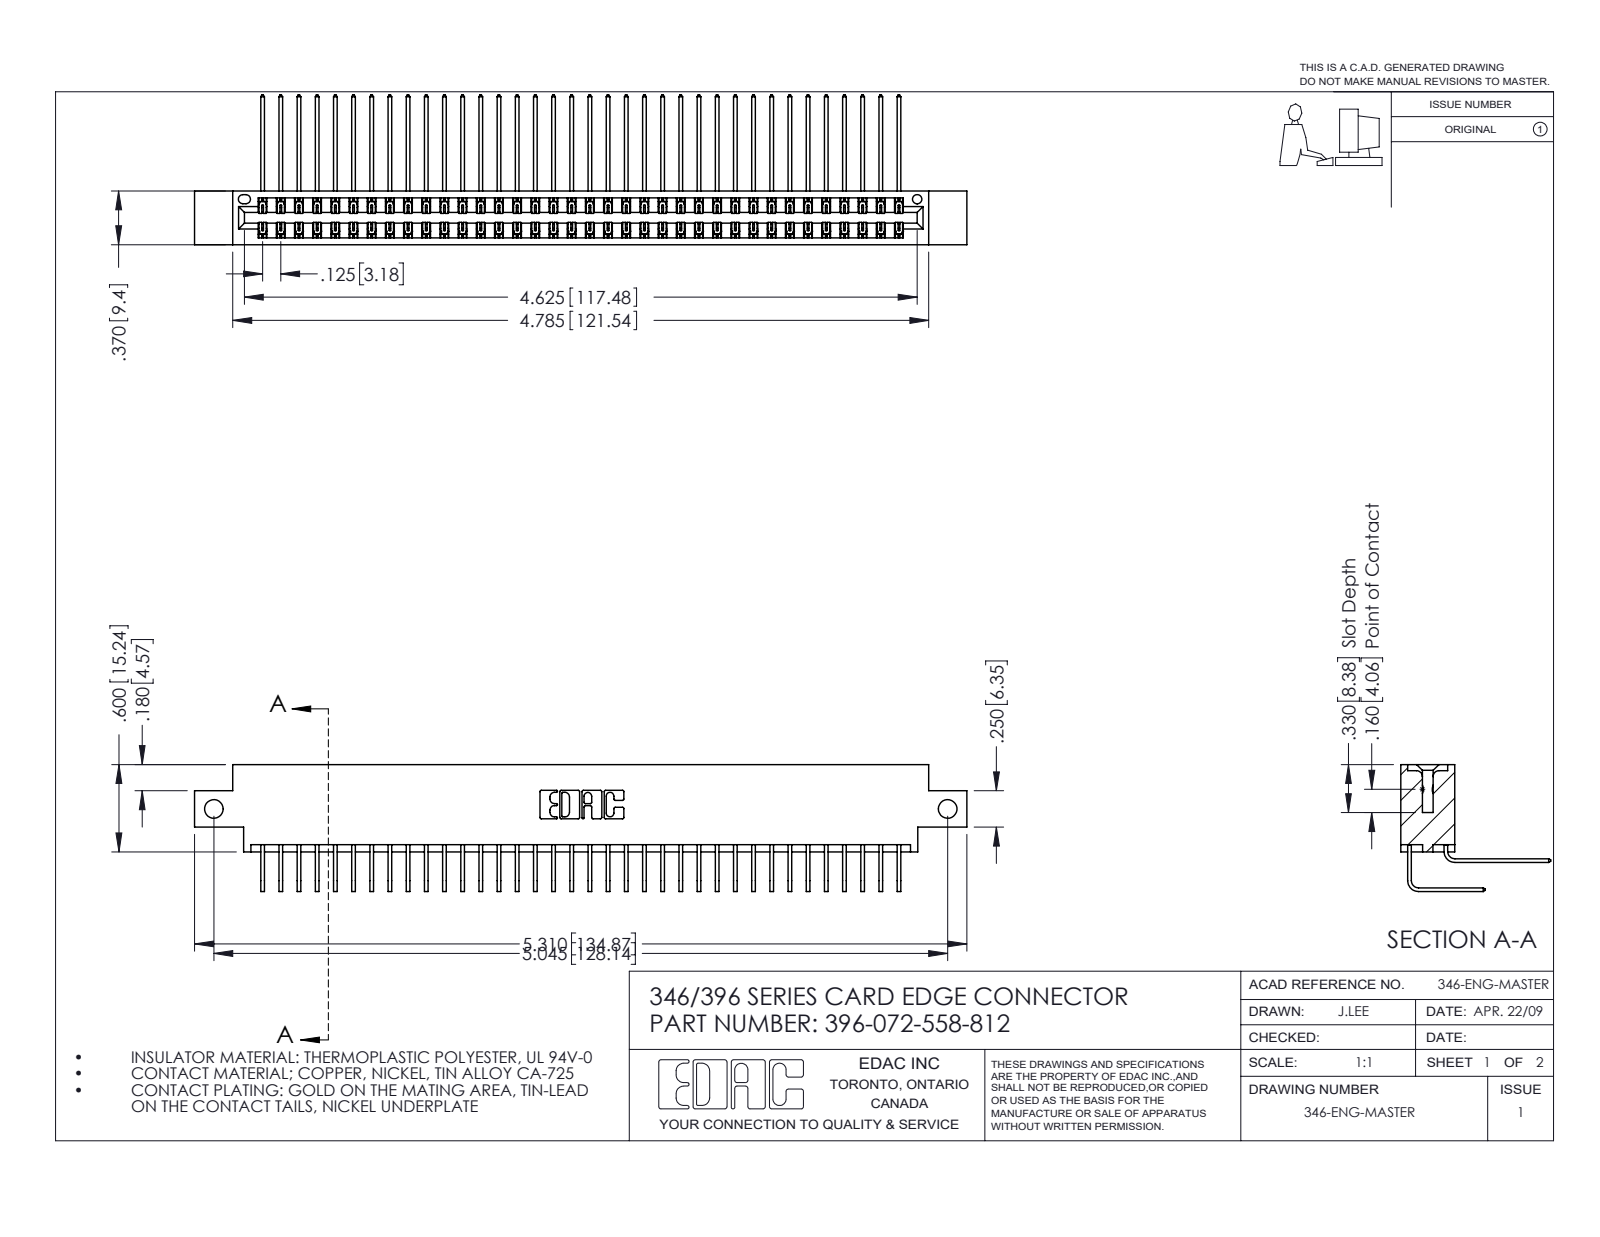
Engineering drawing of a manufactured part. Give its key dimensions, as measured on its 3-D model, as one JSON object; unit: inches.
{"part_name": "396-072-558-812; 345-292-001_558 Tail - 2; 346 Part_0.170 Offset - Side Mount; 345-292-001_558 559 Tail - 1", "step_written_by": "SolidWorks 2016 (CONFIG_CONTROL_DESIGN)", "units": "inches", "bodies": {"solids": 73, "faces": 4014, "planar": 2744, "cylindrical": 1270, "other": 0}, "overall_size": [5.31, 1.03, 0.873], "volume_in3": 0.81, "surface_area_in2": 31.3, "round_holes": [[0.128, 2], [0.064, 1]], "partial_cylinders_radius": [[0.006, 108], [0.01, 22], [0.007, 6], [0.031, 6], [0.026, 3], [0.014, 2], [0.022, 2], [0.024, 2]], "face_to_face_distances": [0.322, 0.048, 0.025, 0.37, 0.25, 0.298, 0.072, 0.275, 0.148, 0.222], "hole_center_spacings": [5.045]}
